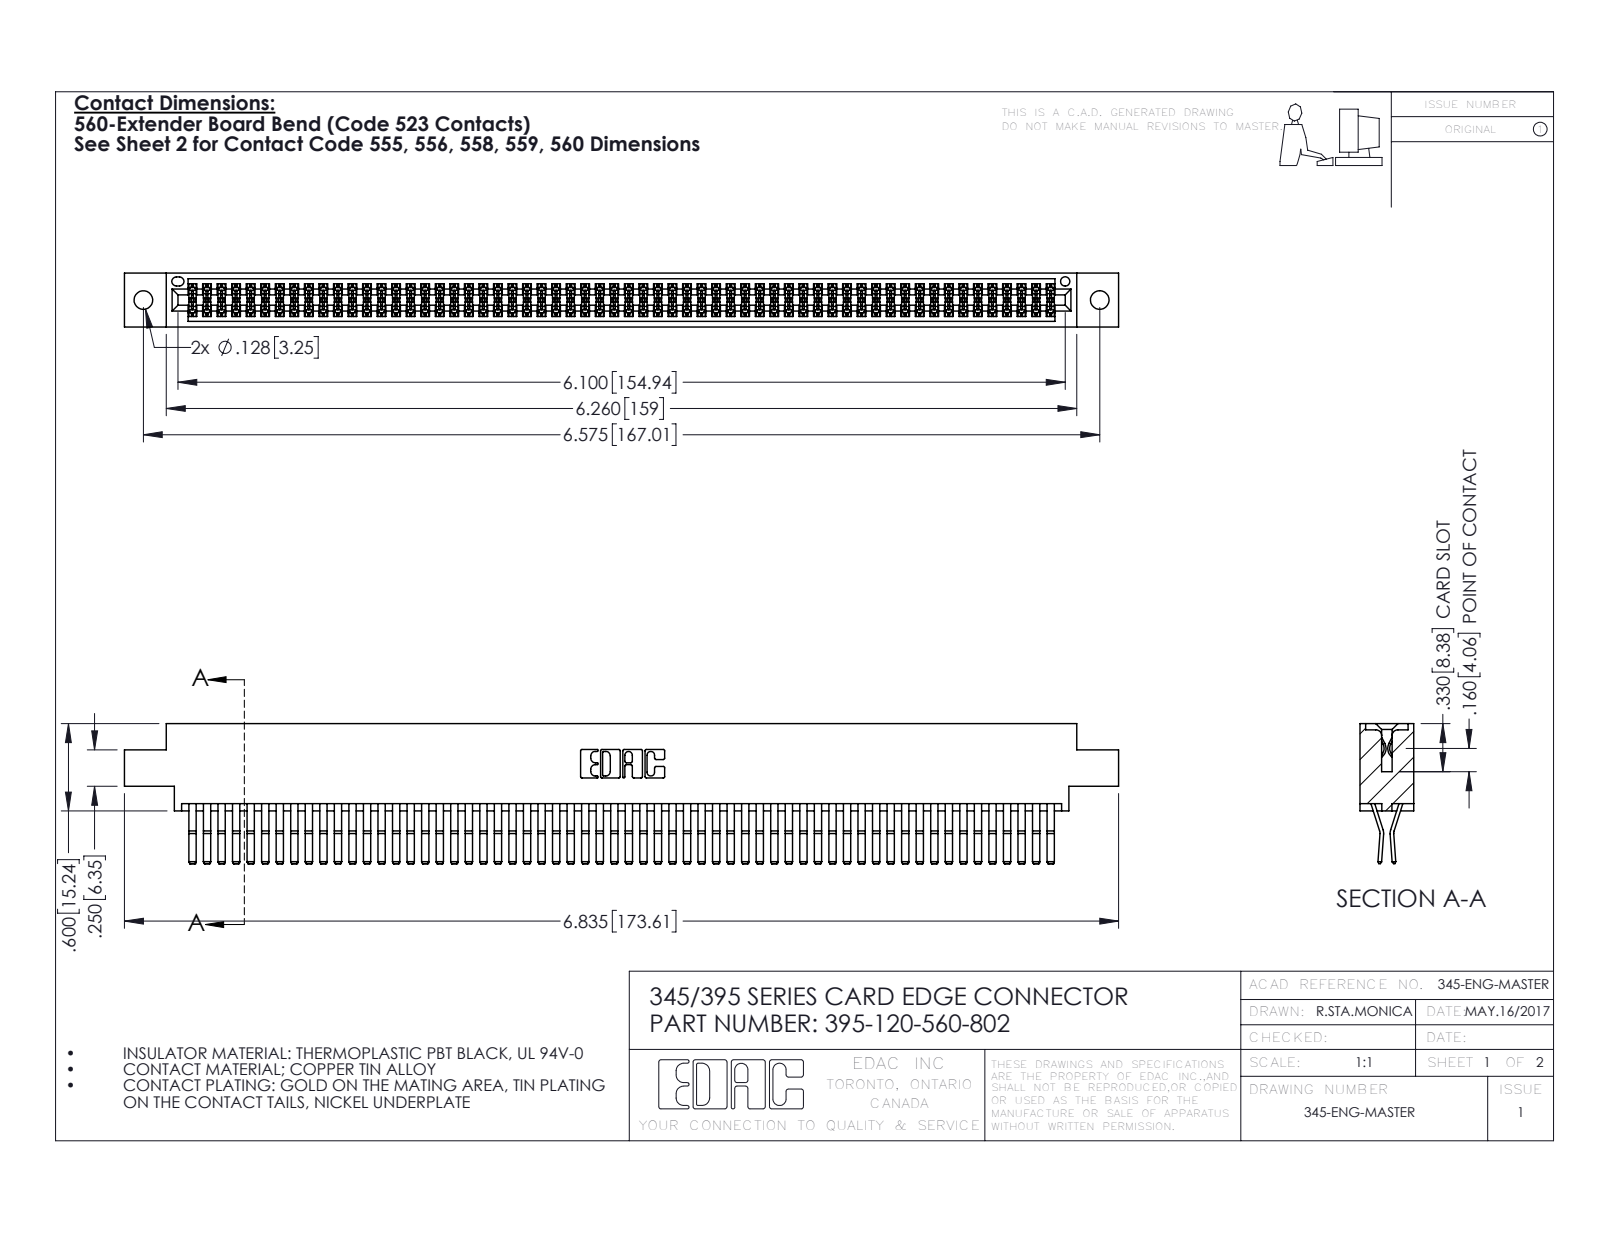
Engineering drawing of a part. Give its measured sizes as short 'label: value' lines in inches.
name: 345-292-001_560 Tail; 395-120-560-802; 345 Part_0.170 Offset - 0.128 Dia
written by: SolidWorks 2016 (CONFIG_CONTROL_DESIGN)
unit: in
bodies: 121 solids, 6370 faces (4044 planar, 2326 cylindrical, 0 other)
size: 6.835 × 0.962 × 0.37
volume: 1.078 in³; area: 43.96 in²
holes: 2× ⌀0.128, 1× ⌀0.064
rounds: 181× R0.006, 22× R0.01, 6× R0.007, 6× R0.031, 3× R0.026, 2× R0.01, 2× R0.014, 2× R0.019
face distances: 0.025, 0.298, 0.072, 0.37, 0.2, 0.098, 0.272, 0.225, 0.175, 0.149
hole spacings: 0.27, 6.339, 6.575
